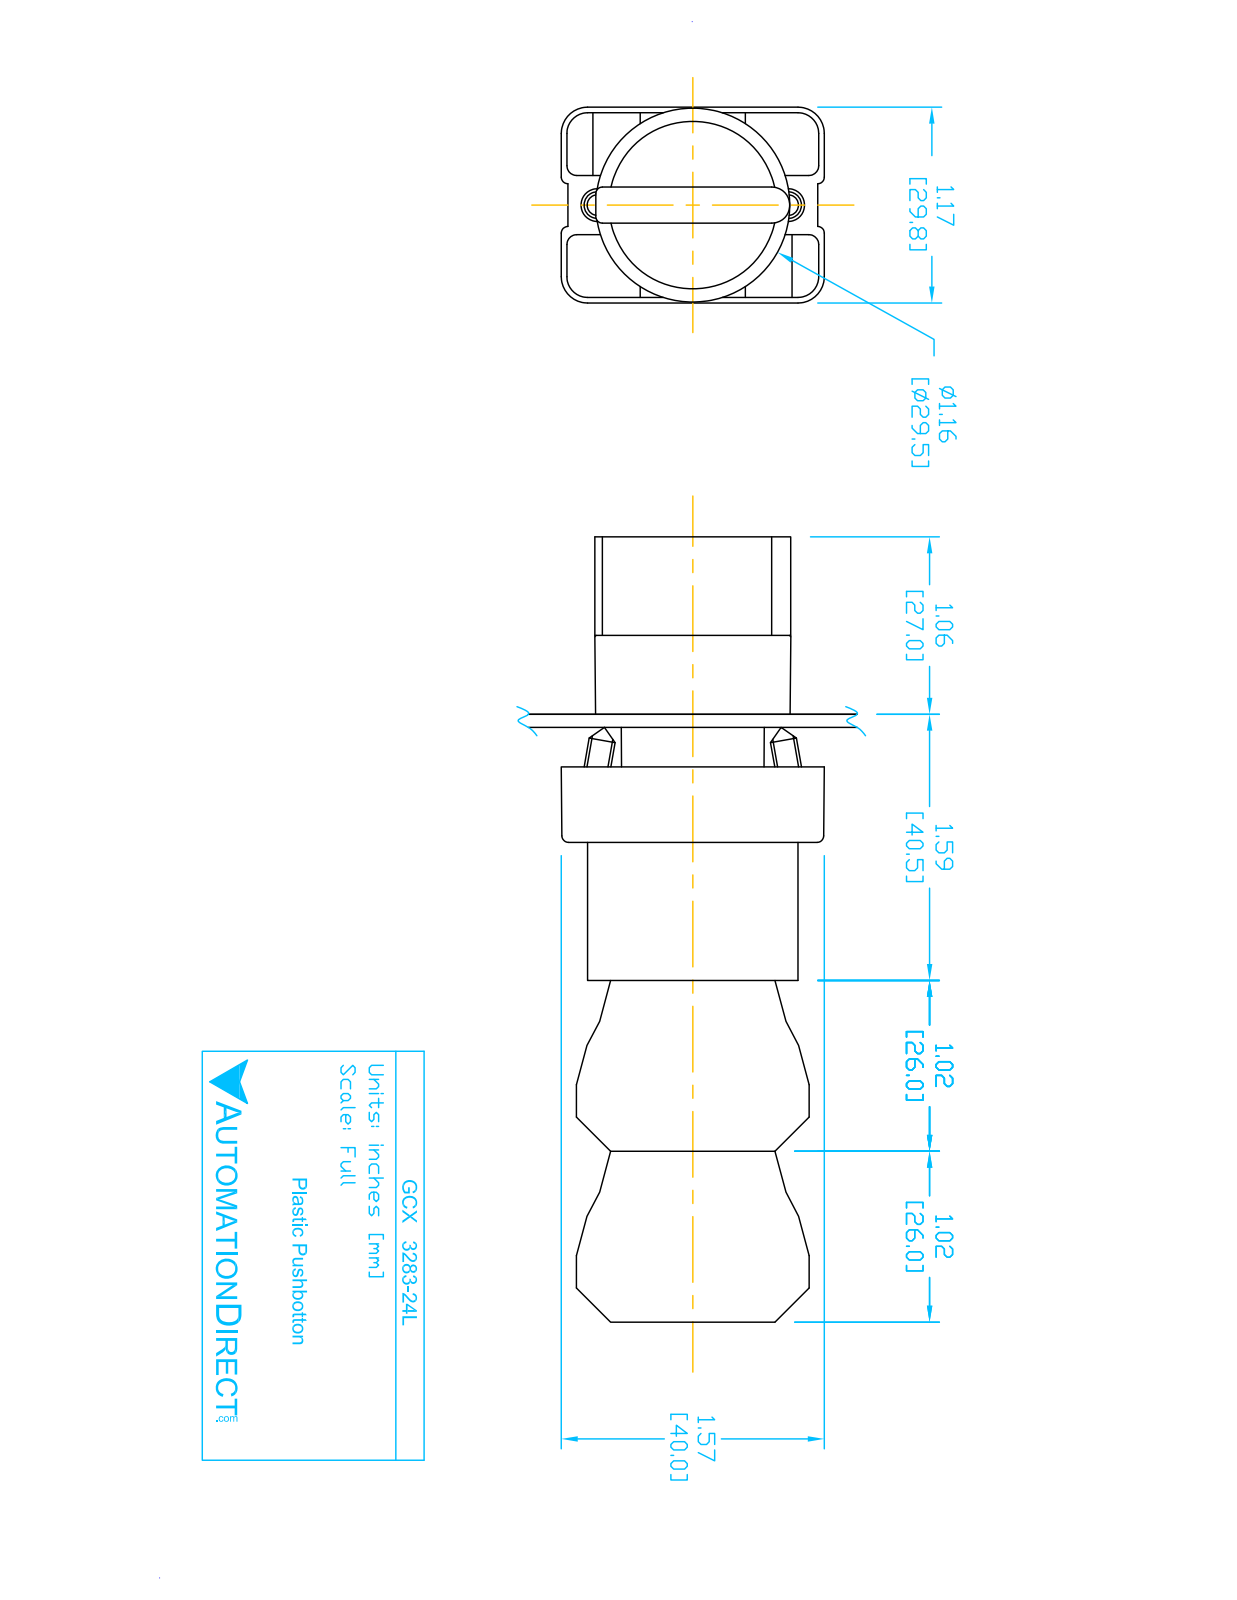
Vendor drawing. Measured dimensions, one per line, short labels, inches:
name: ecx1040; GCX3283L OPERATOR; GCX3283-24L; ECX1050 (+2 more)
written by: SolidWorks 2016 (AUTOMOTIVE_DESIGN)
unit: in
bodies: 11 solids, 724 faces (488 planar, 193 cylindrical, 43 other)
size: 4.677 × 1.581 × 1.177
volume: 4.751 in³; area: 59.22 in²
holes: 4× ⌀0.079, 2× ⌀0.087, 2× ⌀0.124, 2× ⌀0.13, 1× ⌀0.197, 1× ⌀0.469, 1× ⌀0.878, 1× ⌀0.888, 1× ⌀1.024
bosses: 4× ⌀0.157, 1× ⌀1.175, 1× ⌀1.004, 1× ⌀0.945, 1× ⌀0.856, 1× ⌀0.78, 1× ⌀0.504
rounds: 24× R0.059, 12× R0.041, 12× R0.124, 12× R0.157, 9× R0.039, 2× R0.02, 2× R0.063, 2× R0.079
face distances: 0.579, 0.593, 1.024, 1.171, 0.014, 0.827, 1.85, 3.043, 2.02, 1.193
hole spacings: 0.236, 1.003, 0.974, 0.472, 0.539, 0.544, 1.083, 0.484
